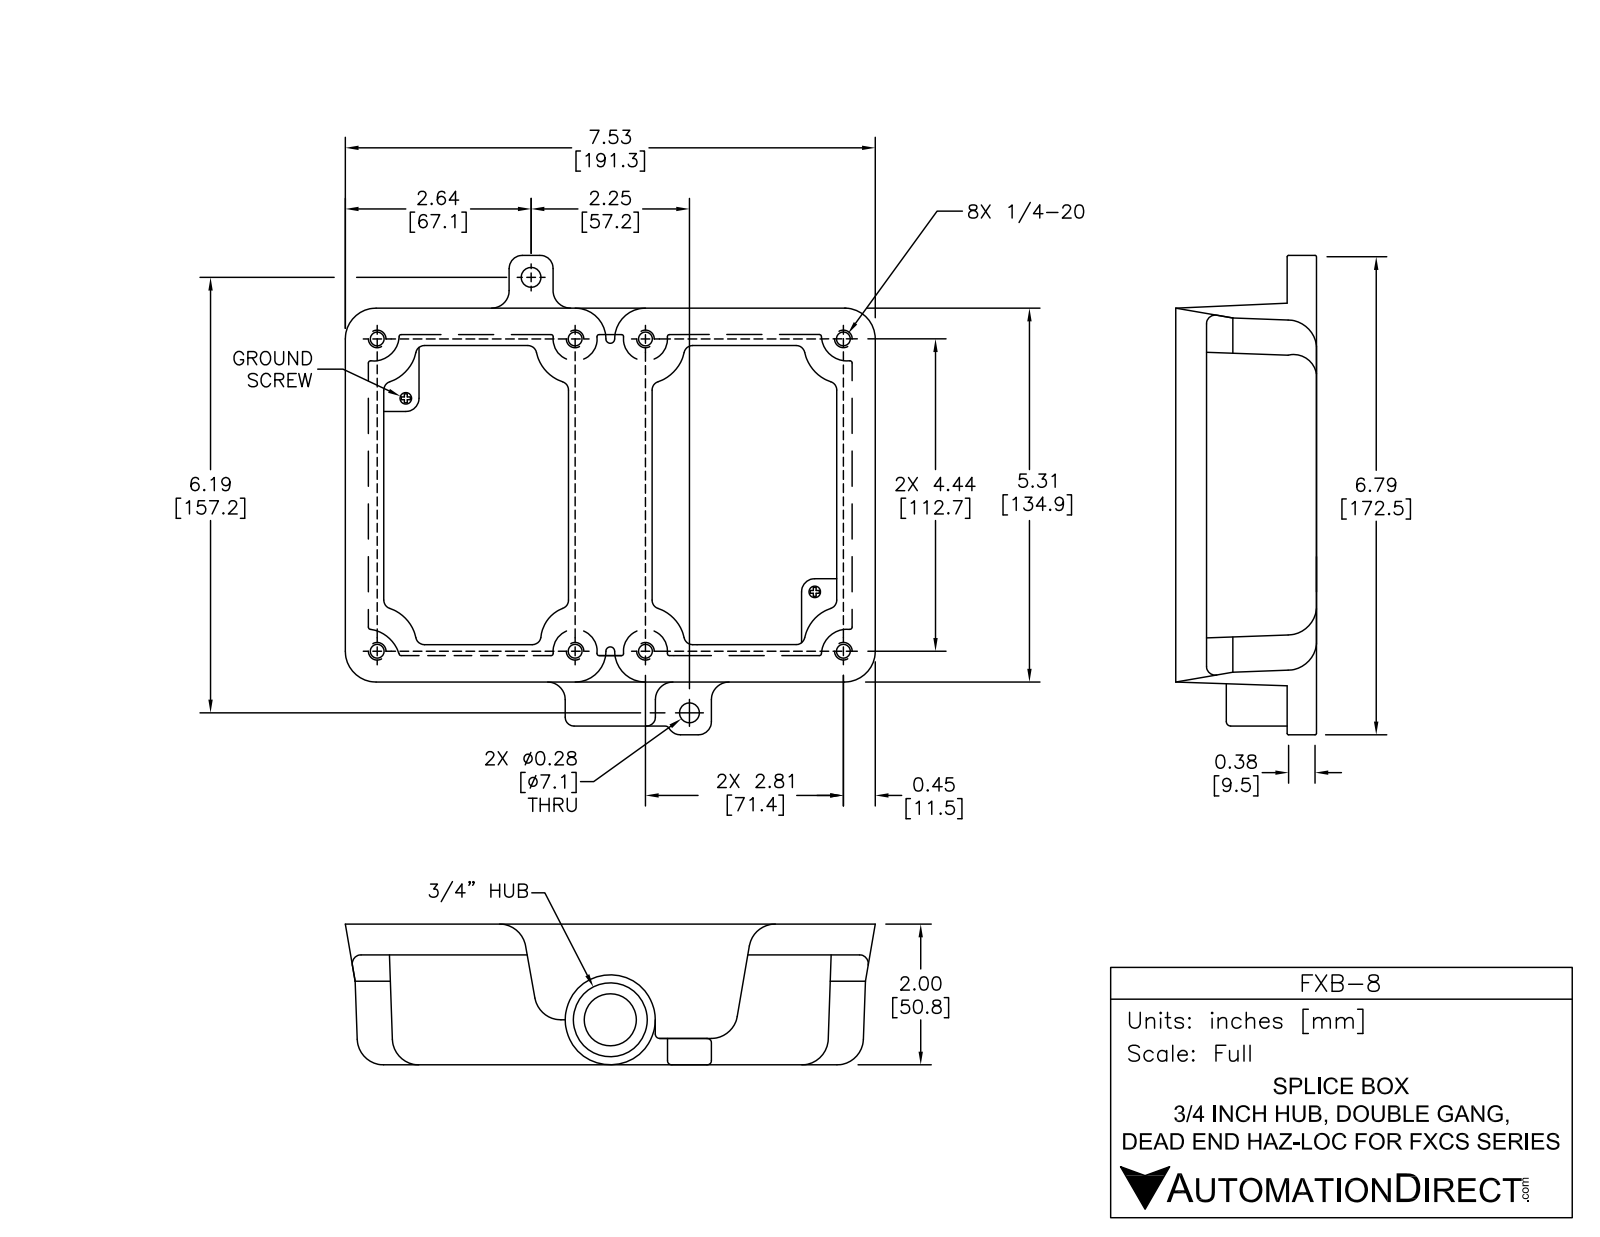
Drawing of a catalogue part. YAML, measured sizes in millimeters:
part_name: "FXB-8"
step_written_by: "SolidWorks 2015 (AUTOMOTIVE_DESIGN)"
units: millimeters
bodies: {solids: 3, faces: 382, planar: 155, cylindrical: 135, other: 92}
overall_size: [191.5, 174, 52.25]
volume: 458258
surface_area: 118959
round_holes:
  - {diameter: 5, count: 8}
  - {diameter: 7, count: 2}
  - {diameter: 14, count: 1}
  - {diameter: 26.67, count: 1}
round_bosses_or_shafts:
  - {diameter: 8, count: 2}
  - {diameter: 12.2, count: 1}
partial_cylinders:
  - {radius: 3, count: 36}
  - {radius: 4.5, count: 16}
  - {radius: 9, count: 8}
  - {radius: 12.75, count: 8}
  - {radius: 2, count: 7}
  - {radius: 4, count: 6}
  - {radius: 6, count: 4}
  - {radius: 7.1, count: 3}
face_to_face_distances: [7.5, 44.75, 52.25, 14.13, 121.87, 107.74, 136, 12.75, 32, 39.5]
hole_center_spacings: [95.75, 112.5, 133.3, 71.49, 71.51, 115.08, 136.04, 146.72]
